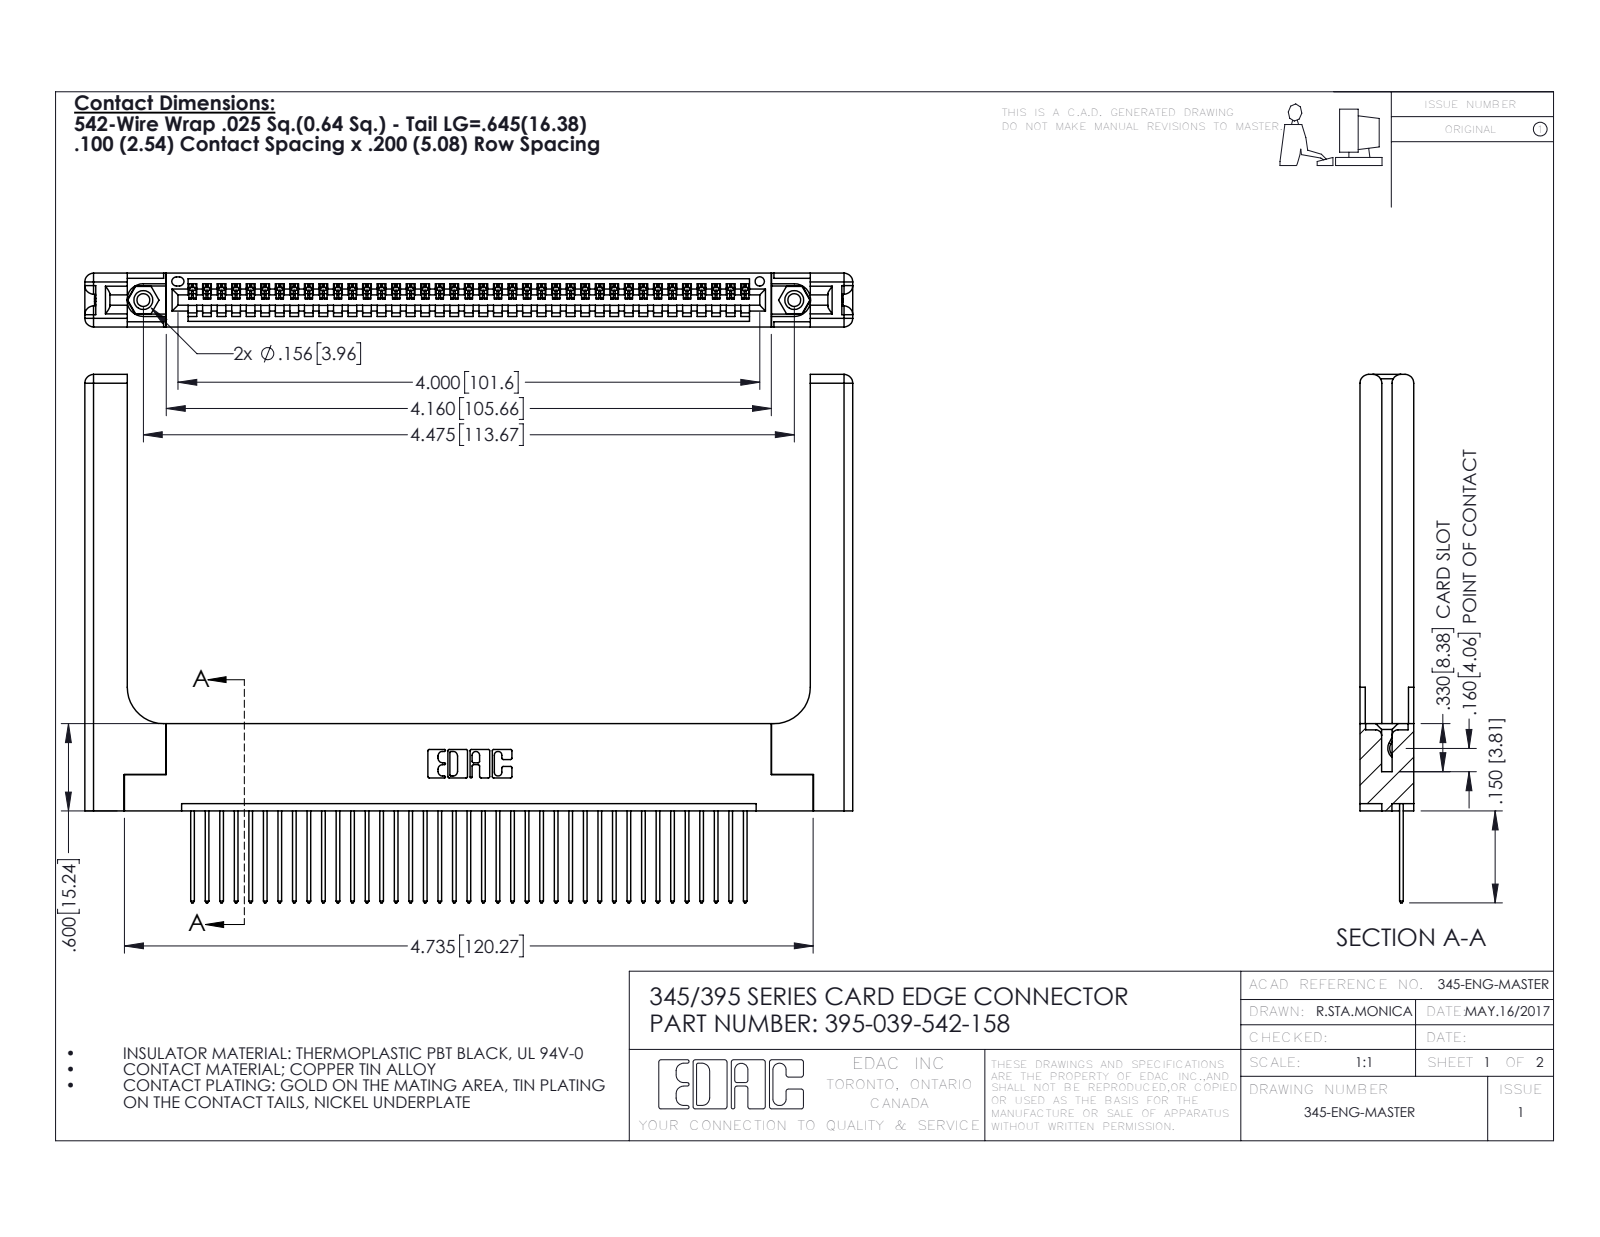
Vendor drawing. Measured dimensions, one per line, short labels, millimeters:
name: 395-039-542-158; 345-220-058_345-220-058; 345-250-001_345-250-001-102; 345-292-001_345-293-142 (+1 more)
written by: SolidWorks 2016 (CONFIG_CONTROL_DESIGN)
unit: mm
bodies: 44 solids, 2644 faces (1788 planar, 796 cylindrical, 60 other)
size: 134.1 × 92.3 × 9.4
volume: 21 300 mm³; area: 22 820 mm²
holes: 2× ⌀2.3, 2× ⌀3.2, 2× ⌀4, 1× ⌀1.6
bosses: 2× ⌀3.9
rounds: 78× R0.2, 78× R0.3, 22× R0.3, 16× R1.5, 6× R0.2, 6× R0.8, 3× R0.7, 2× R0.8
face distances: 1.8, 9.4, 7.6, 5.1, 2.5, 6.9, 0.6, 3.8, 3.8, 5.7
hole spacings: 6.9, 107.7, 113.7
